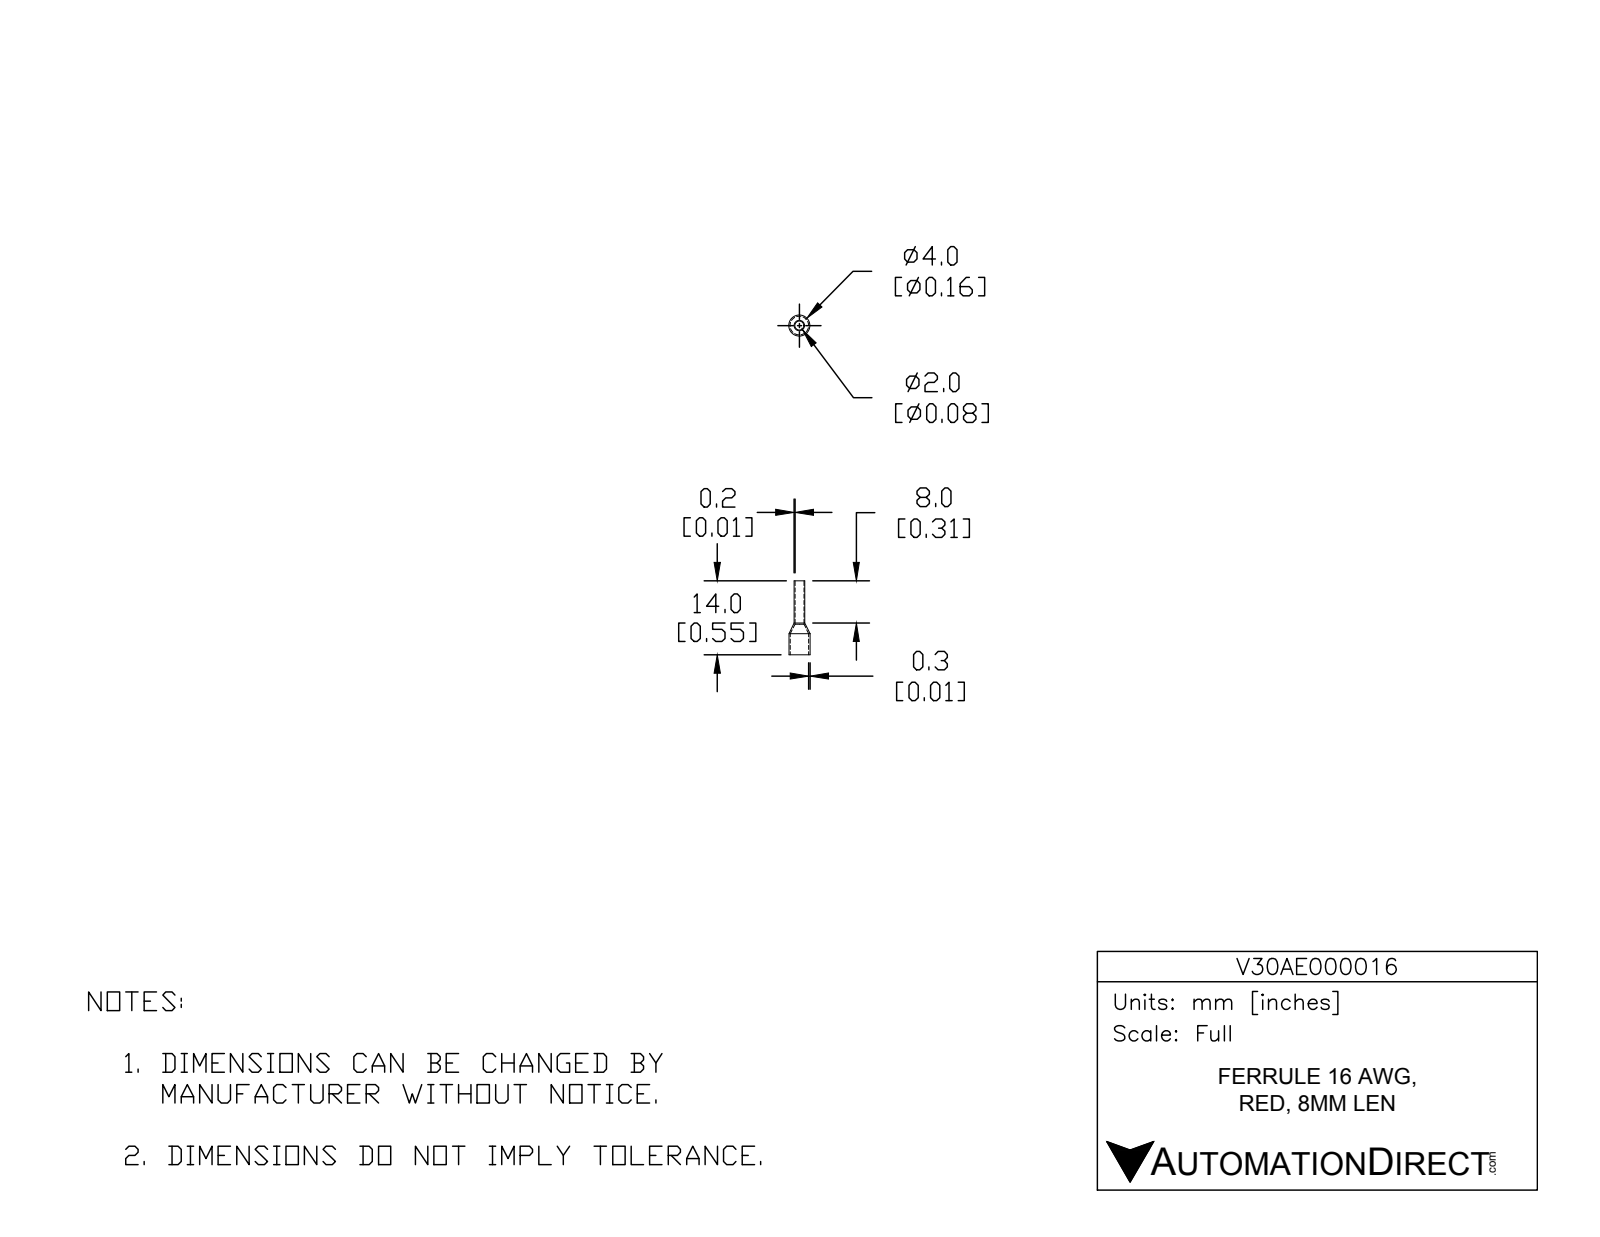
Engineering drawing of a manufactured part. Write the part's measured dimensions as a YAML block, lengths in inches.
part_name: "V30AE000016"
step_written_by: "SolidWorks 2017 (AUTOMOTIVE_DESIGN)"
units: inches
bodies: {solids: 1, faces: 14, planar: 2, cylindrical: 8, other: 4}
overall_size: [0.551, 0.157, 0.157]
volume: 0.001
surface_area: 0.357
round_holes:
  - {diameter: 0.067, count: 1}
  - {diameter: 0.138, count: 1}
round_bosses_or_shafts:
  - {diameter: 0.157, count: 1}
  - {diameter: 0.079, count: 1}
face_to_face_distances: [0.551]
